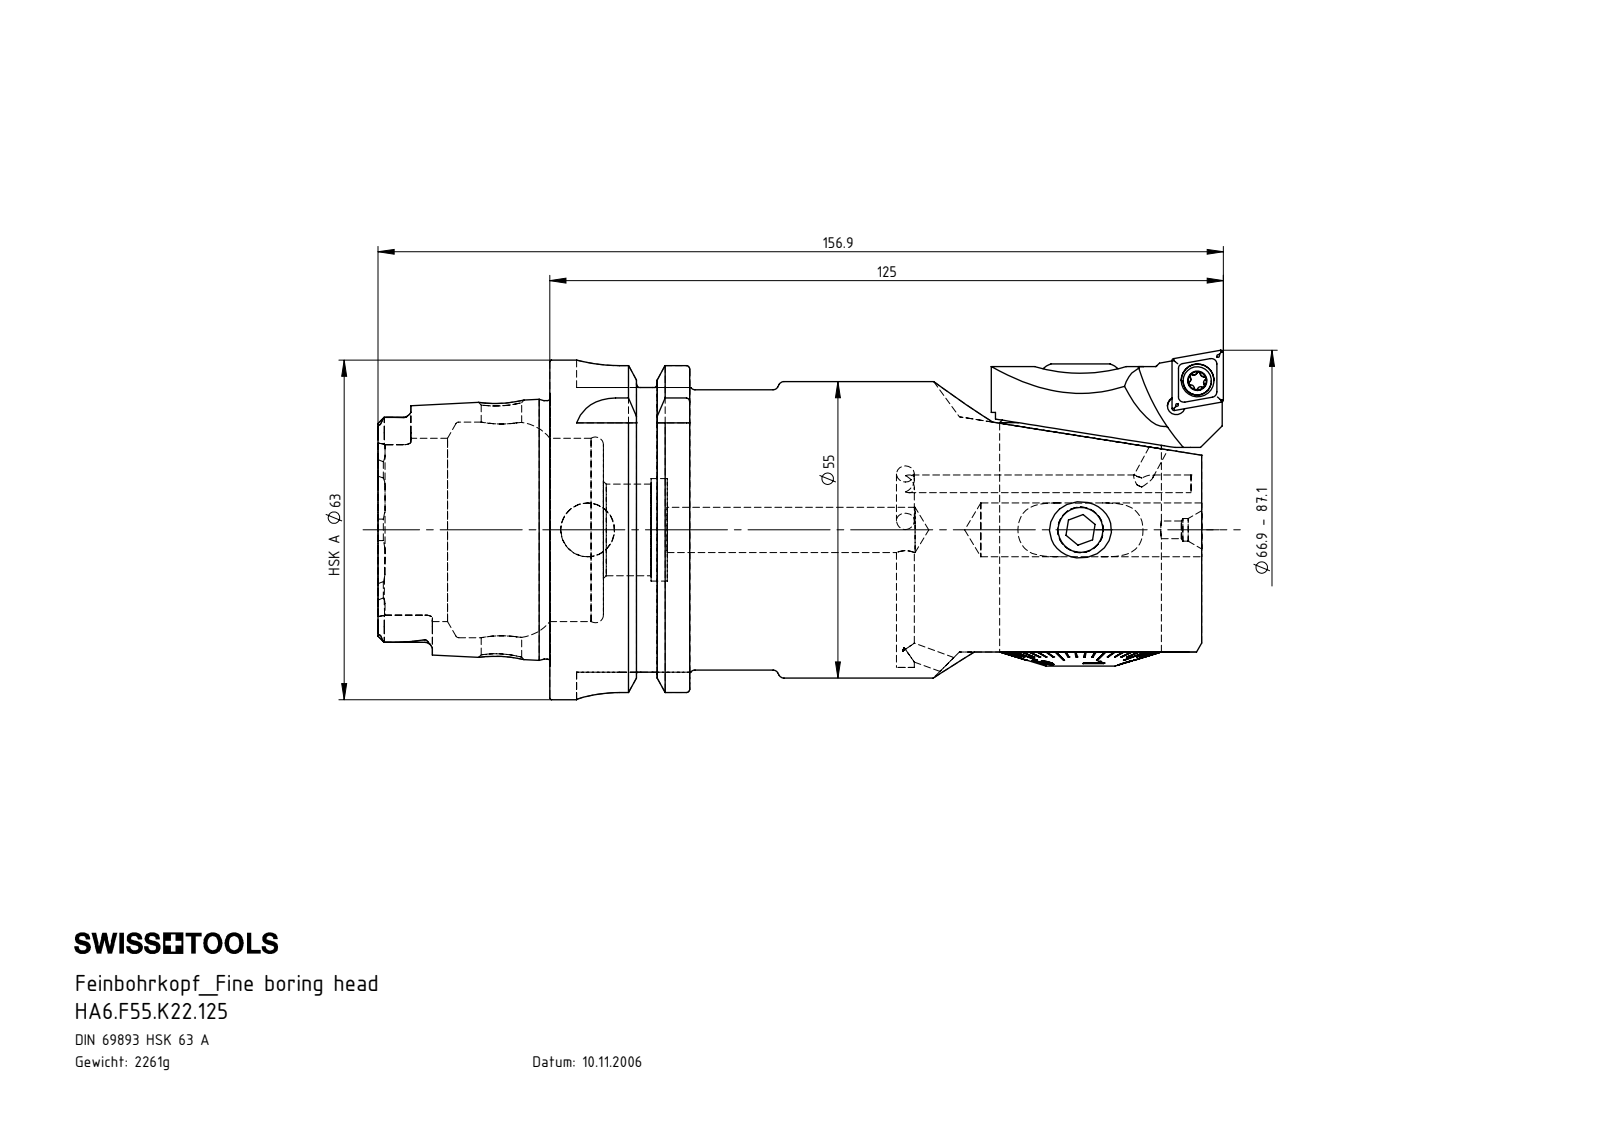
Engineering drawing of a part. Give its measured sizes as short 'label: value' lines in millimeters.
name: A55-BG2.011.016_D; F55-BG2.014.015_B; F55-ER1.101.016_A; A55-BG3.011.033_A_gekürzt (+8 more)
written by: SolidWorks 2022 (CONFIG_CONTROL_DESIGN)
unit: mm
bodies: 16 solids, 976 faces (373 planar, 208 cylindrical, 395 other)
size: 156.9 × 65 × 63
volume: 288 432 mm³; area: 63 953 mm²
holes: 9× ⌀3.3, 2× ⌀8.5, 2× ⌀10, 2× ⌀17, 1× ⌀4.2, 1× ⌀4.4, 1× ⌀5, 1× ⌀6.1, 1× ⌀7.5, 1× ⌀8, 1× ⌀8.4, 1× ⌀11
bosses: 2× ⌀10, 2× ⌀5.25, 2× ⌀4, 1× ⌀63, 1× ⌀55, 1× ⌀54.95, 1× ⌀52, 1× ⌀47.94
rounds: 12× R0.34, 12× R0.59, 6× R1.4, 4× R0.5, 4× R2.88, 4× R8, 3× R3.2, 2× R10
face distances: 121, 16, 2.5, 25.95, 95.05, 1.18, 41.89, 9.95, 111.05, 7.07
hole spacings: 5.73, 5.86, 9.74, 14.5, 21, 32.5, 75, 91.5
